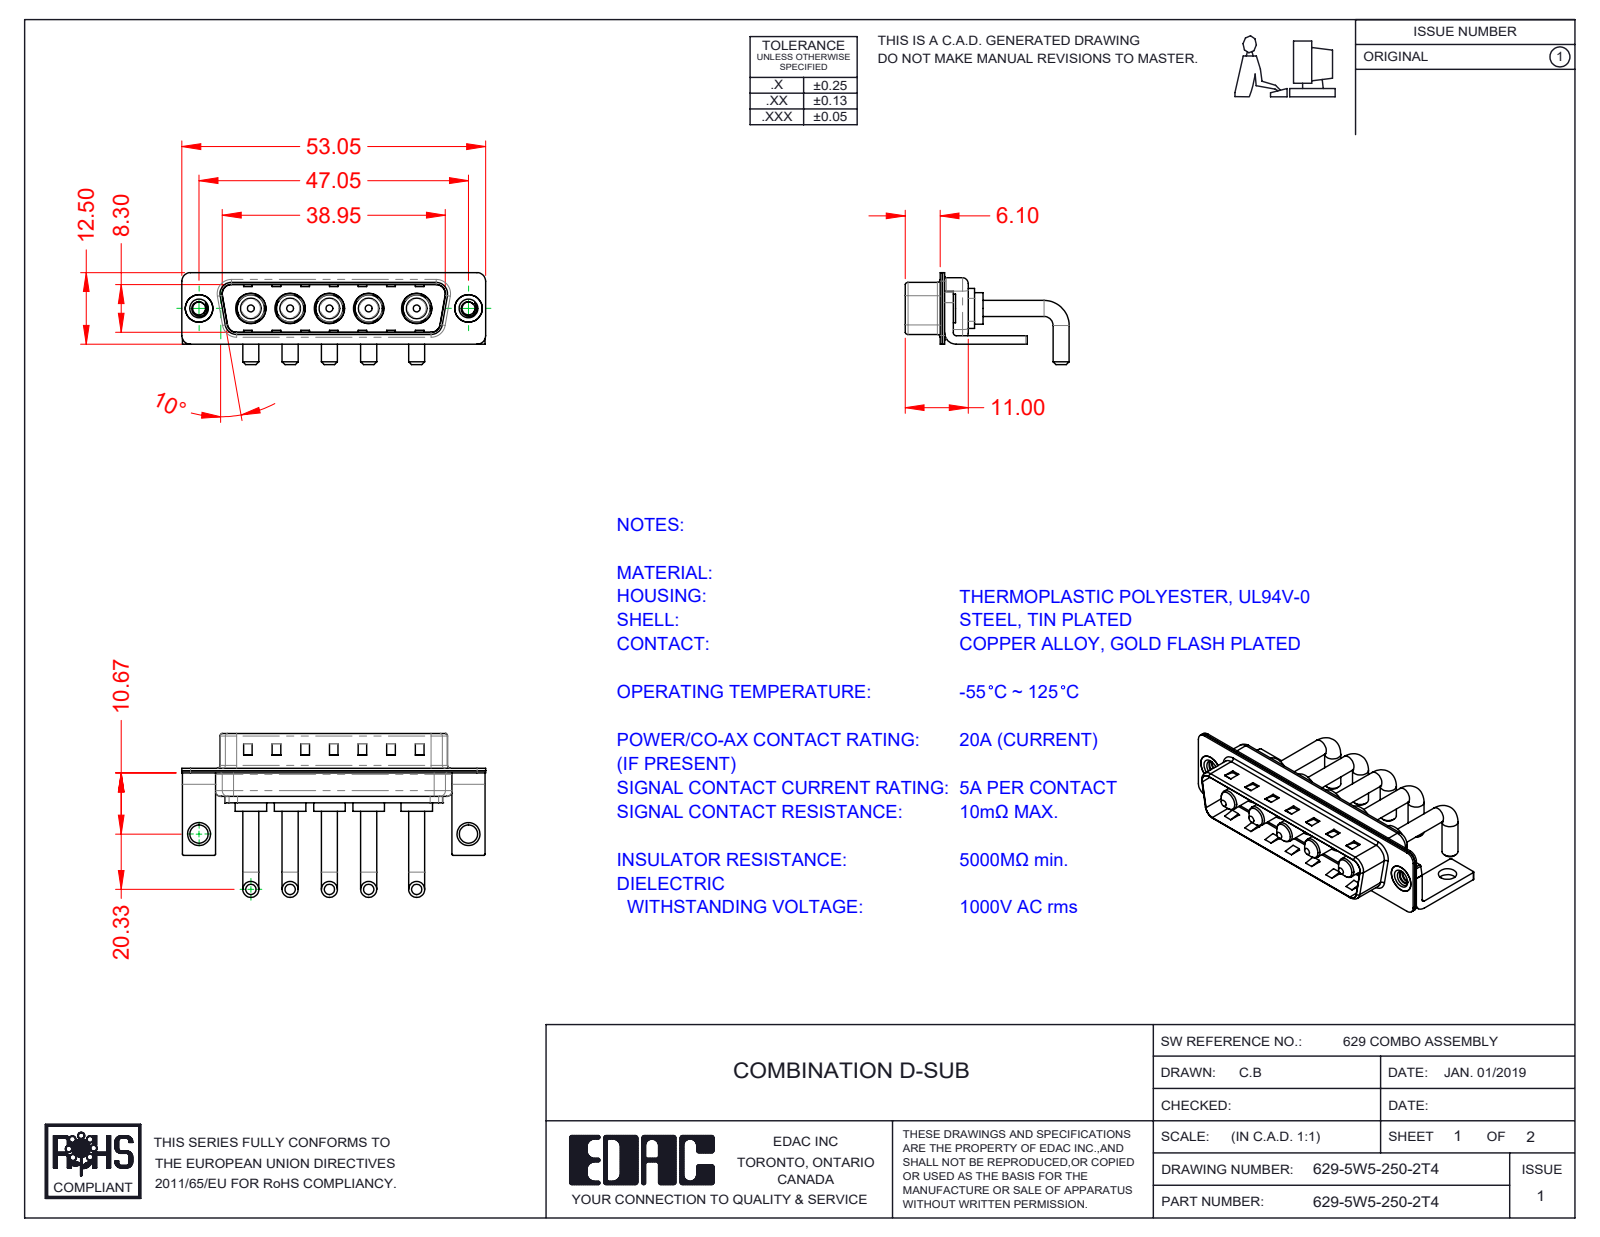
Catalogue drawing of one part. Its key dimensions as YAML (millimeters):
part_name: "629-5W5-250-2T4; 629Combo Threaded Rivet_3; 629Combo Shell Front_25 Contacts; 629Combo Stabilizer Bracket (+3 more)"
step_written_by: "SolidWorks 2020 (CONFIG_CONTROL_DESIGN)"
units: millimeters
bodies: {solids: 17, faces: 631, planar: 241, cylindrical: 260, other: 130}
overall_size: [53.05, 28.63, 16.05]
volume: 3889
surface_area: 8046
round_holes:
  - {diameter: 4.85, count: 5}
  - {diameter: 5.3, count: 5}
  - {diameter: 2.26, count: 2}
  - {diameter: 3.2, count: 2}
  - {diameter: 4, count: 2}
  - {diameter: 4.8, count: 2}
round_bosses_or_shafts:
  - {diameter: 2.8, count: 10}
  - {diameter: 5.5, count: 5}
  - {diameter: 5.2, count: 5}
  - {diameter: 4.75, count: 5}
  - {diameter: 3.75, count: 5}
  - {diameter: 3.6, count: 5}
  - {diameter: 5, count: 2}
  - {diameter: 4.9, count: 2}
partial_cylinders:
  - {radius: 0.25, count: 16}
  - {radius: 1.5, count: 16}
  - {radius: 2, count: 13}
  - {radius: 0.5, count: 9}
  - {radius: 1.6, count: 8}
  - {radius: 2.1, count: 5}
  - {radius: 0.6, count: 4}
  - {radius: 0.65, count: 4}
face_to_face_distances: [0.4, 0.8, 1.5, 9.5, 9.1, 8.7, 9.9, 5.2, 0.75, 1.2]
hole_center_spacings: [6.86, 13.73, 47.05, 6.85, 6.87, 8.37, 8.38, 9.04]
